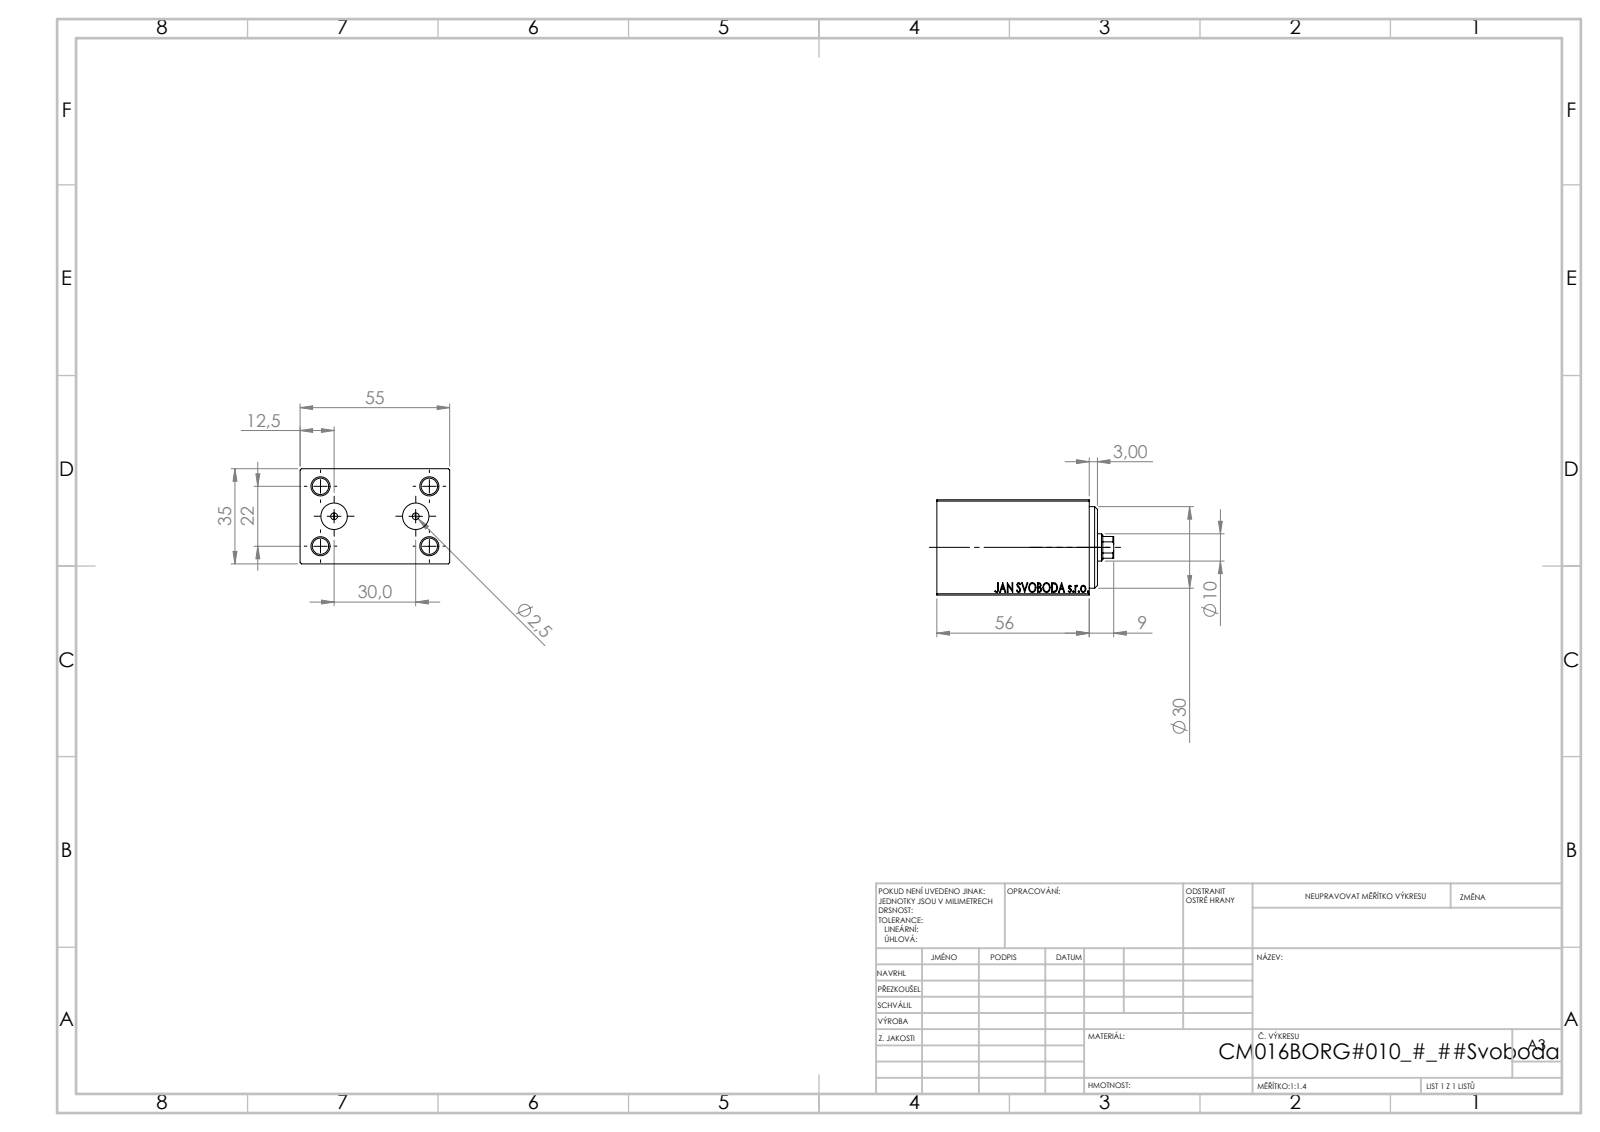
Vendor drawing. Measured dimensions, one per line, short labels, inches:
name: V450CM_B_Body; V450CM_VC_B; V450CM_B_VCP
written by: SolidWorks 2019 (CONFIG_CONTROL_DESIGN)
unit: in
bodies: 3 solids, 877 faces (401 planar, 50 cylindrical, 426 other)
size: 2.559 × 2.165 × 1.378
volume: 6.367 in³; area: 38.93 in²
holes: 4× ⌀0.236, 2× ⌀0.098, 2× ⌀0.383, 1× ⌀0.177, 1× ⌀0.394, 1× ⌀0.531, 1× ⌀0.571, 1× ⌀0.63, 1× ⌀0.709, 1× ⌀1.181
rounds: 1× R0.177
face distances: 1.378, 2.165, 0.197, 2.008, 2.205, 1.811, 0.315, 0.118, 2.323, 2.126
hole spacings: 0.476, 0.899, 1.444, 0.591, 0.866, 1.575, 1.797, 1.181
